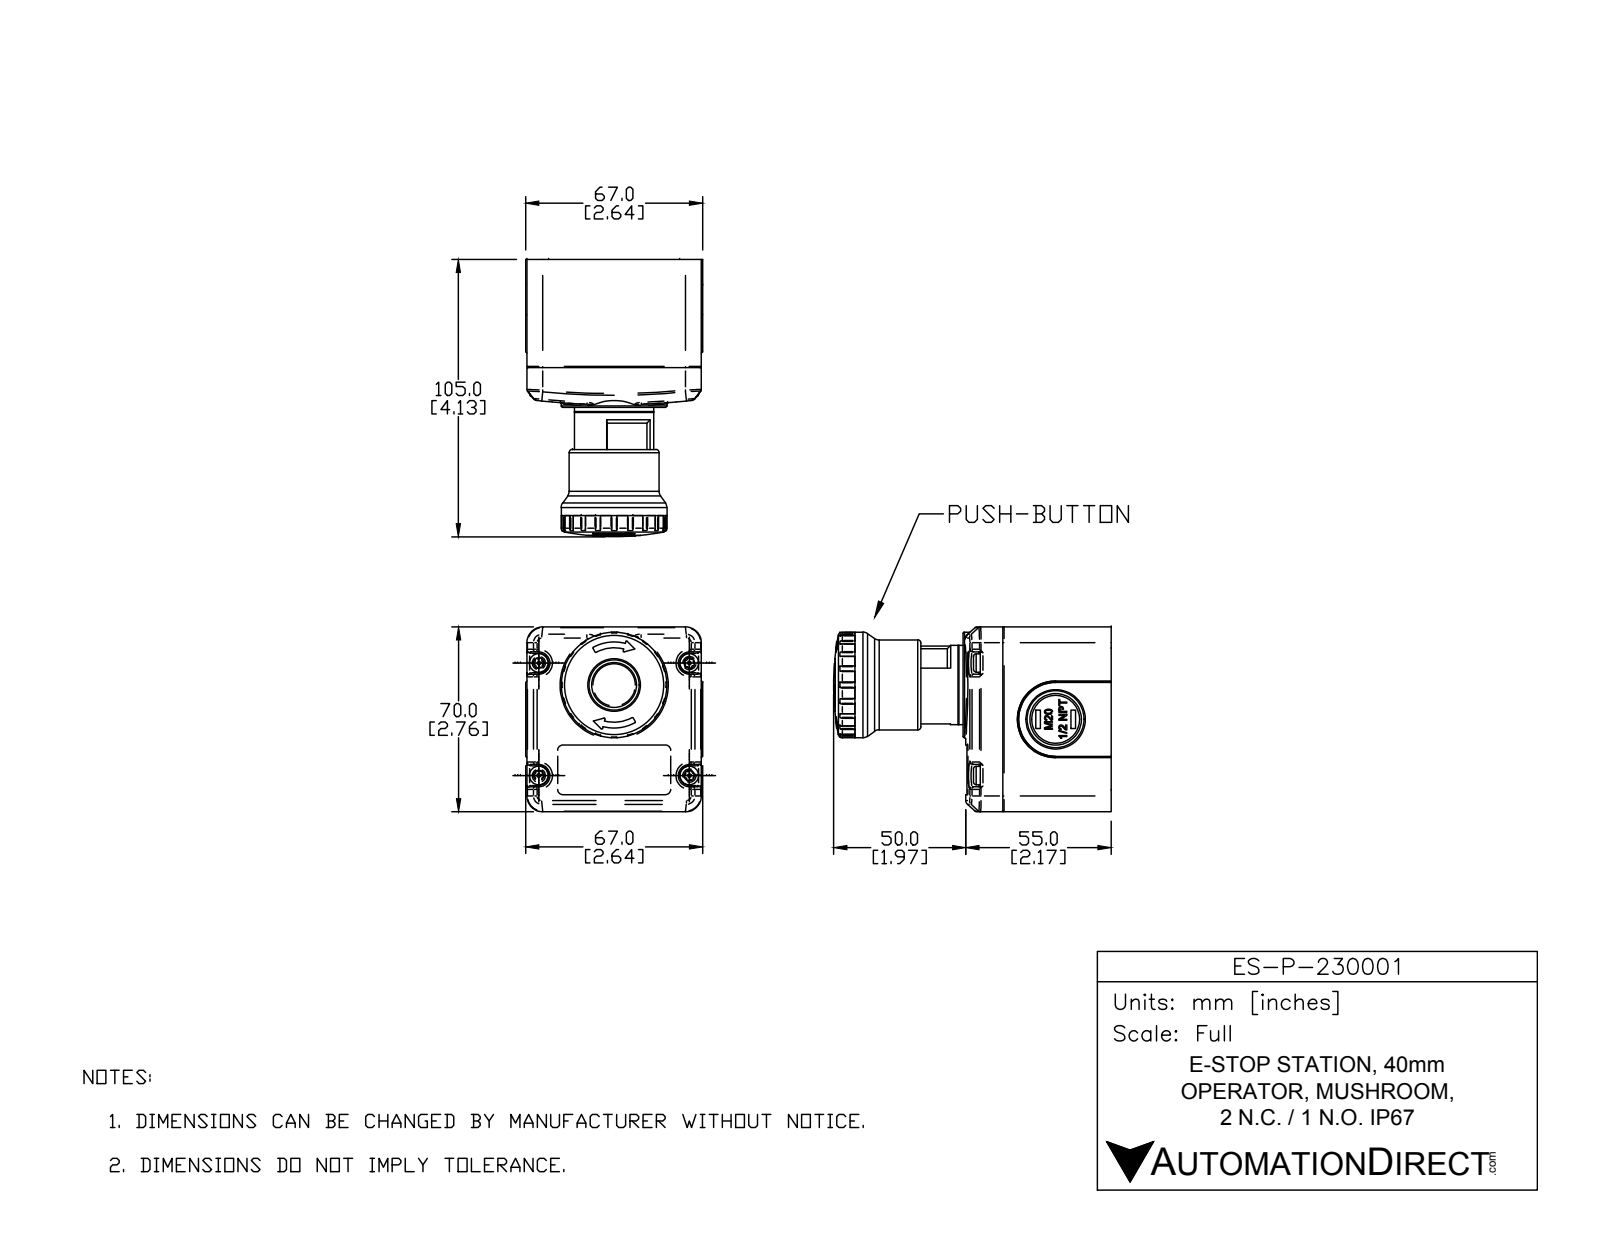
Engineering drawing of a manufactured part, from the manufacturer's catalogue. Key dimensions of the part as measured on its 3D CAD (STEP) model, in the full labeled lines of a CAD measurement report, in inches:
Part name (STEP PRODUCT): ES-P-230001
STEP written by: SolidWorks 2016 (AUTOMOTIVE_DESIGN)
Units: inches
Bodies: 11 solids, 990 faces (353 planar, 286 cylindrical, 351 other)
Overall size (bounding box): 4.134 × 2.756 × 2.638
Volume: 17.36 in³ · Surface area: 75.57 in²
Round holes (diameter × count): ⌀0.173 ×4, ⌀0.846 ×1, ⌀1.224 ×1
Round bosses / shafts (diameter × count): ⌀0.276 ×4, ⌀0.039 ×4, ⌀1.575 ×1, ⌀1.339 ×1, ⌀1.181 ×1, ⌀0.787 ×1
Partial cylindrical surfaces — rounded edges, fillets, slot ends (radius × count): R0.004 ×80, R0.03 ×24, R0.02 ×14, R0.039 ×8, R0.079 ×6, R0.008 ×4, R0.165 ×4, R0.236 ×4
Main face-to-face distances: 1.583, 2.756, 2.598, 2.173, 0.591, 0.02, 0.079, 2.52, 2.236, 0.654
Hole centre spacings: 1.235, 1.966, 2.126, 2.283, 3.12
